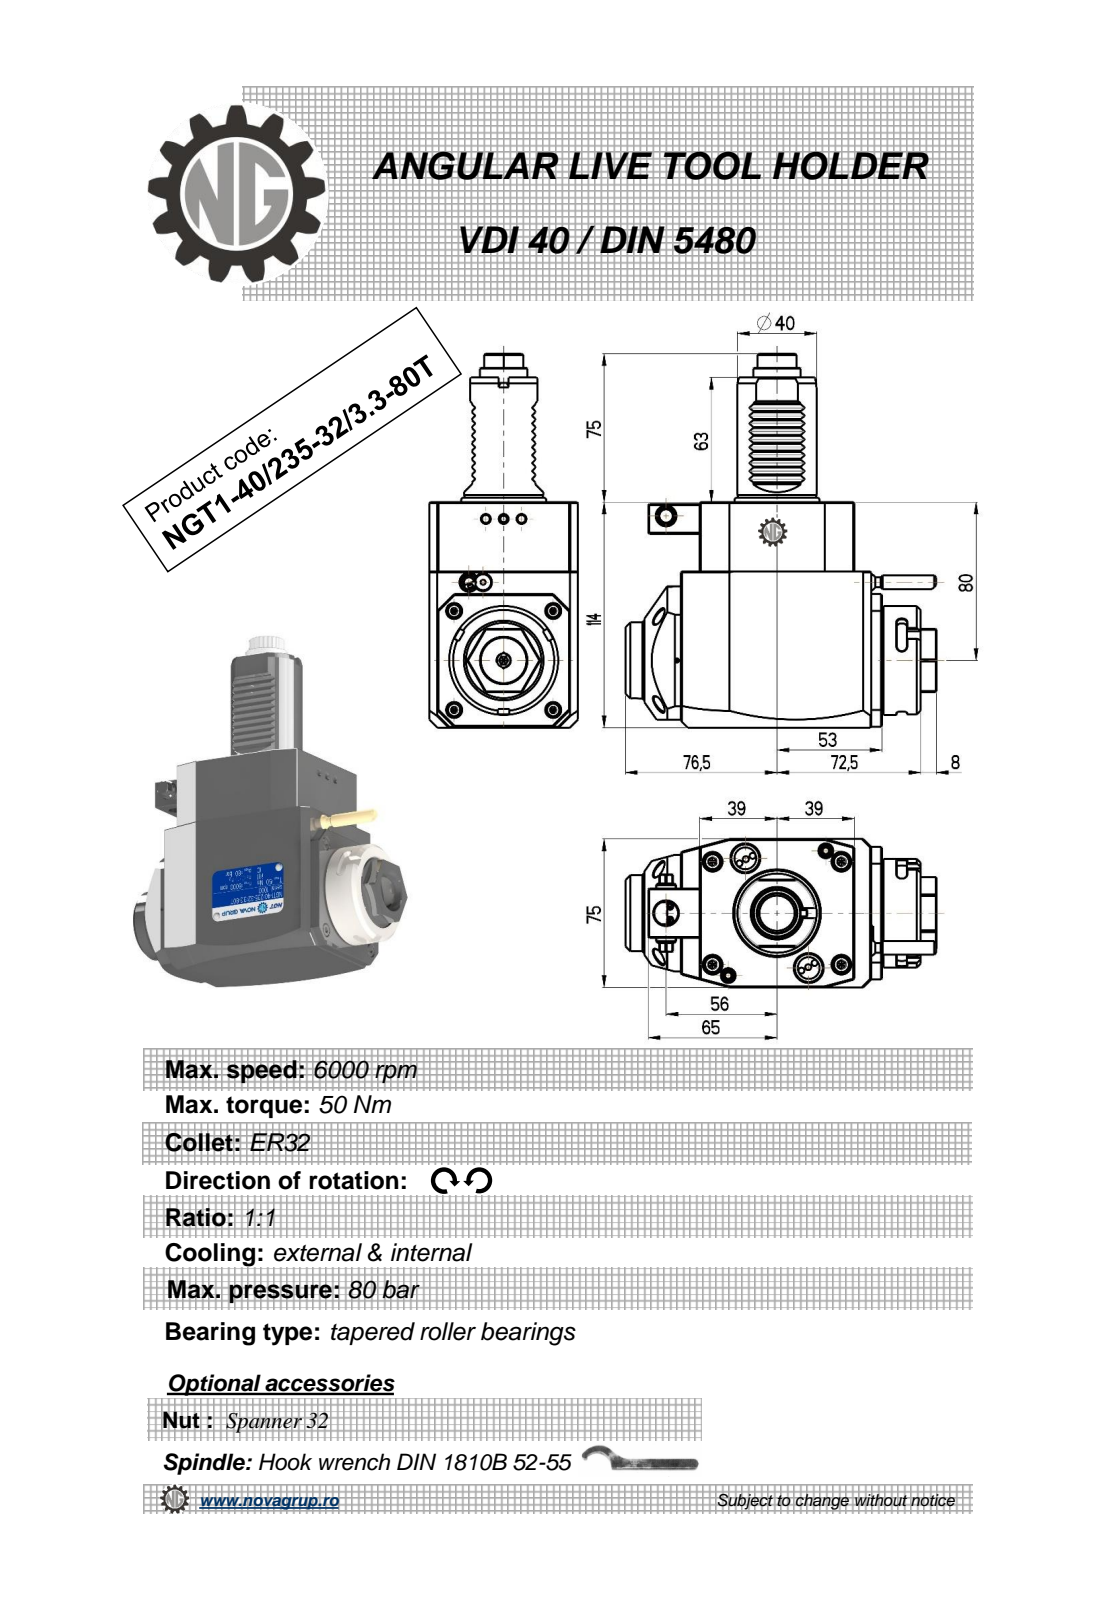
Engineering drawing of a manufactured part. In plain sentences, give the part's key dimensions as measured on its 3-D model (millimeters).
The part is named "NGT1_40_235_32_3_3_80T". Its 3-D file was written by "PRO/ENGINEER BY PARAMETRIC TECHNOLOGY CORPORATION, 2010280 (CONFIG_CONTROL_DESIGN)". It is 1 solid with 512 faces: 228 planar, 184 cylindrical and 100 other. Overall it measures 189 by 157 by 75 millimeters. Its volume is 972 350 cubic millimeters and its surface area 73 164 square millimeters. Round holes: 1 of diameter 2.5, 1 of diameter 3, 1 of diameter 9.5, 1 of diameter 12, 1 of diameter 23. Round bosses or shafts: 2 of diameter 8, 1 of diameter 55, 1 of diameter 48, 1 of diameter 40, 1 of diameter 38.5, 1 of diameter 24, 1 of diameter 10, 1 of diameter 7. Partial cylindrical surfaces (rounded edges, fillets, slot ends): 48 of radius 2.08, 20 of radius 0.3, 6 of radius 2.5, 2 of radius 180, 1 of radius 3.85, 1 of radius 4.25, 1 of radius 9.08, 1 of radius 9.92. The main face-to-face distances are 75, 114, 14, 78, 92, 79, 25, 19.5, 111.5, 33.5. The hole center spacings are 36.47, 43.2, 71.5.
